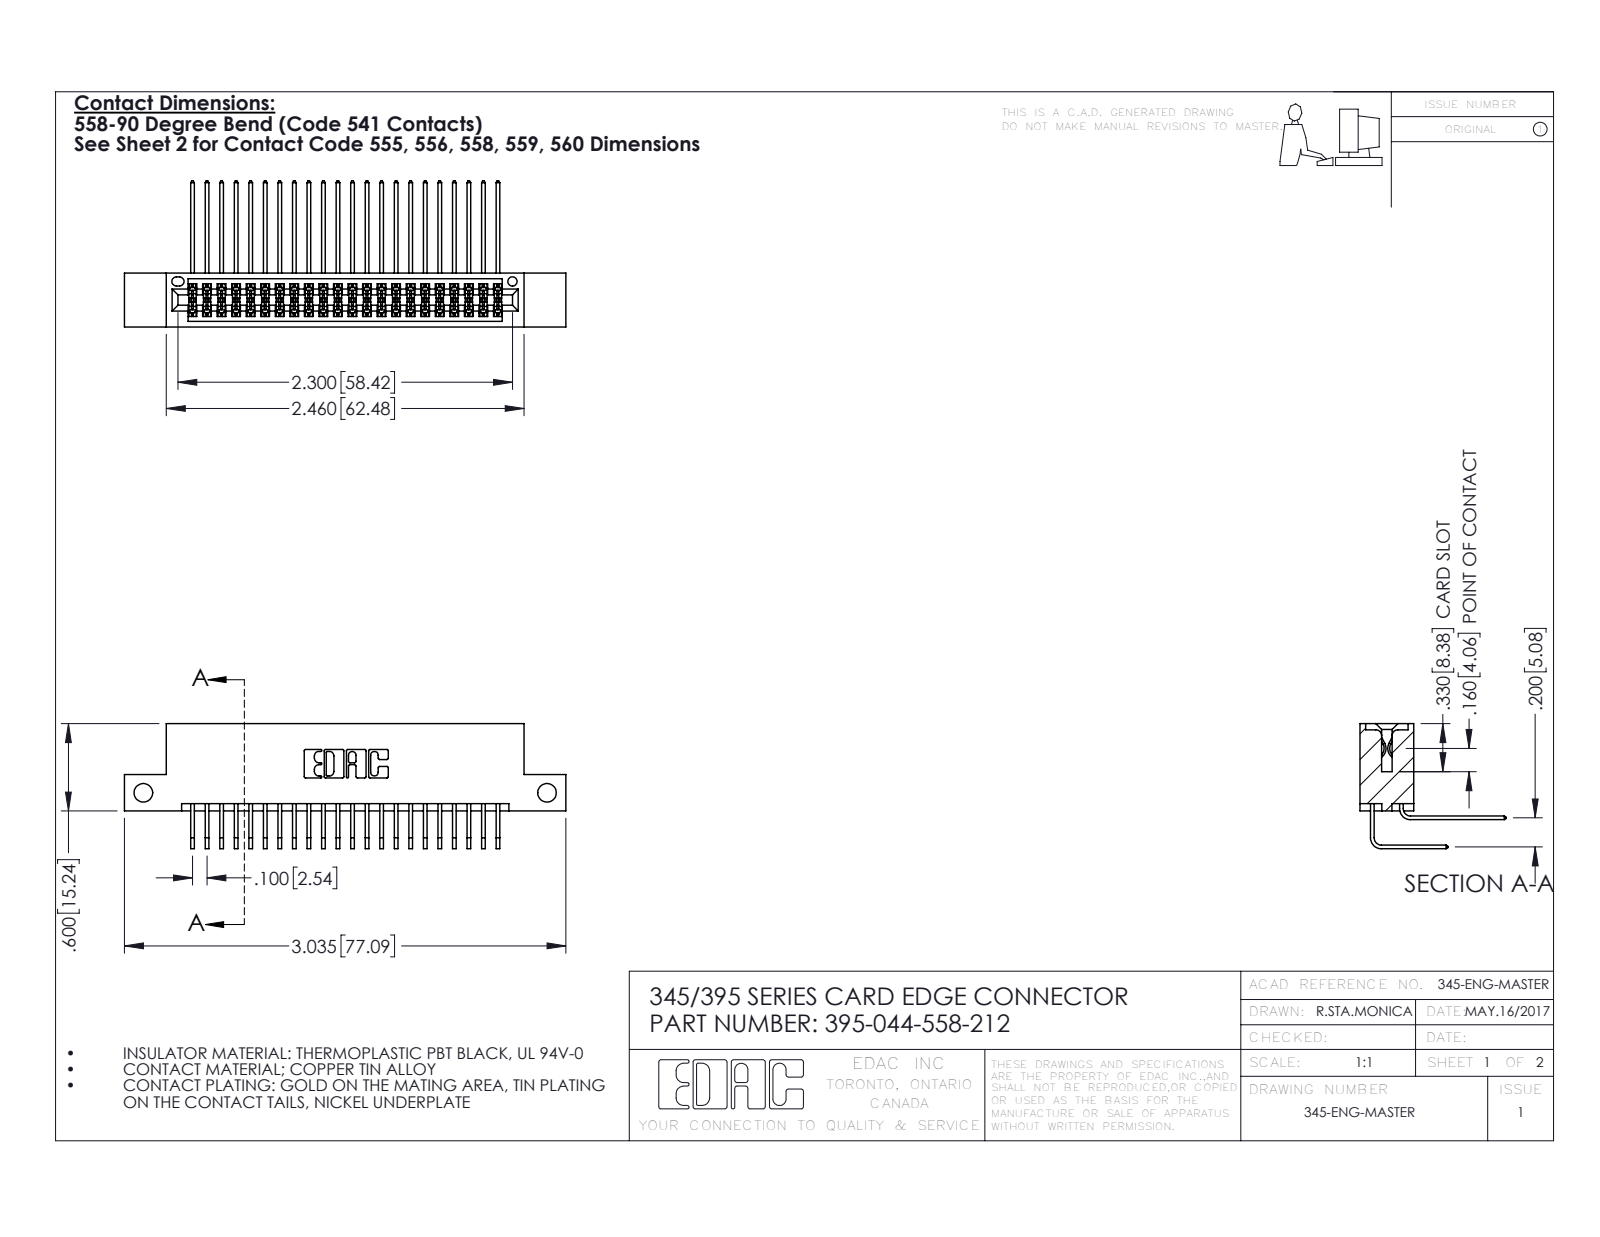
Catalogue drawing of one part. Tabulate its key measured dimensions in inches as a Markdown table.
| quantity | value |
| --- | --- |
| part name | 345-292-001_558 Tail - 2; 345 Part_Flush Mounting Lugs - Side Mount; 395-044-558-212; 345-292-001_558 559 Tail - 1 |
| STEP written by | SolidWorks 2016 (CONFIG_CONTROL_DESIGN) |
| units | inches |
| bodies | 45 solids, 2414 faces (1620 planar, 794 cylindrical, 0 other) |
| overall size | 3.035 × 1.005 × 0.859 |
| volume | 0.456 in³ |
| surface area | 18.15 in² |
| round holes (diameter × count) | 0.128 × 2, 0.064 × 1 |
| partial cylindrical surfaces (radius × count) | 0.006 × 67, 0.01 × 22, 0.007 × 6, 0.031 × 6, 0.026 × 3, 0.014 × 2, 0.019 × 2, 0.022 × 2 |
| main face-to-face distances | 0.2, 0.072, 0.298, 0.37, 0.098, 0.272, 0.025, 0.225, 0.285, 0.025 |
| hole center spacings | 2.775 |
